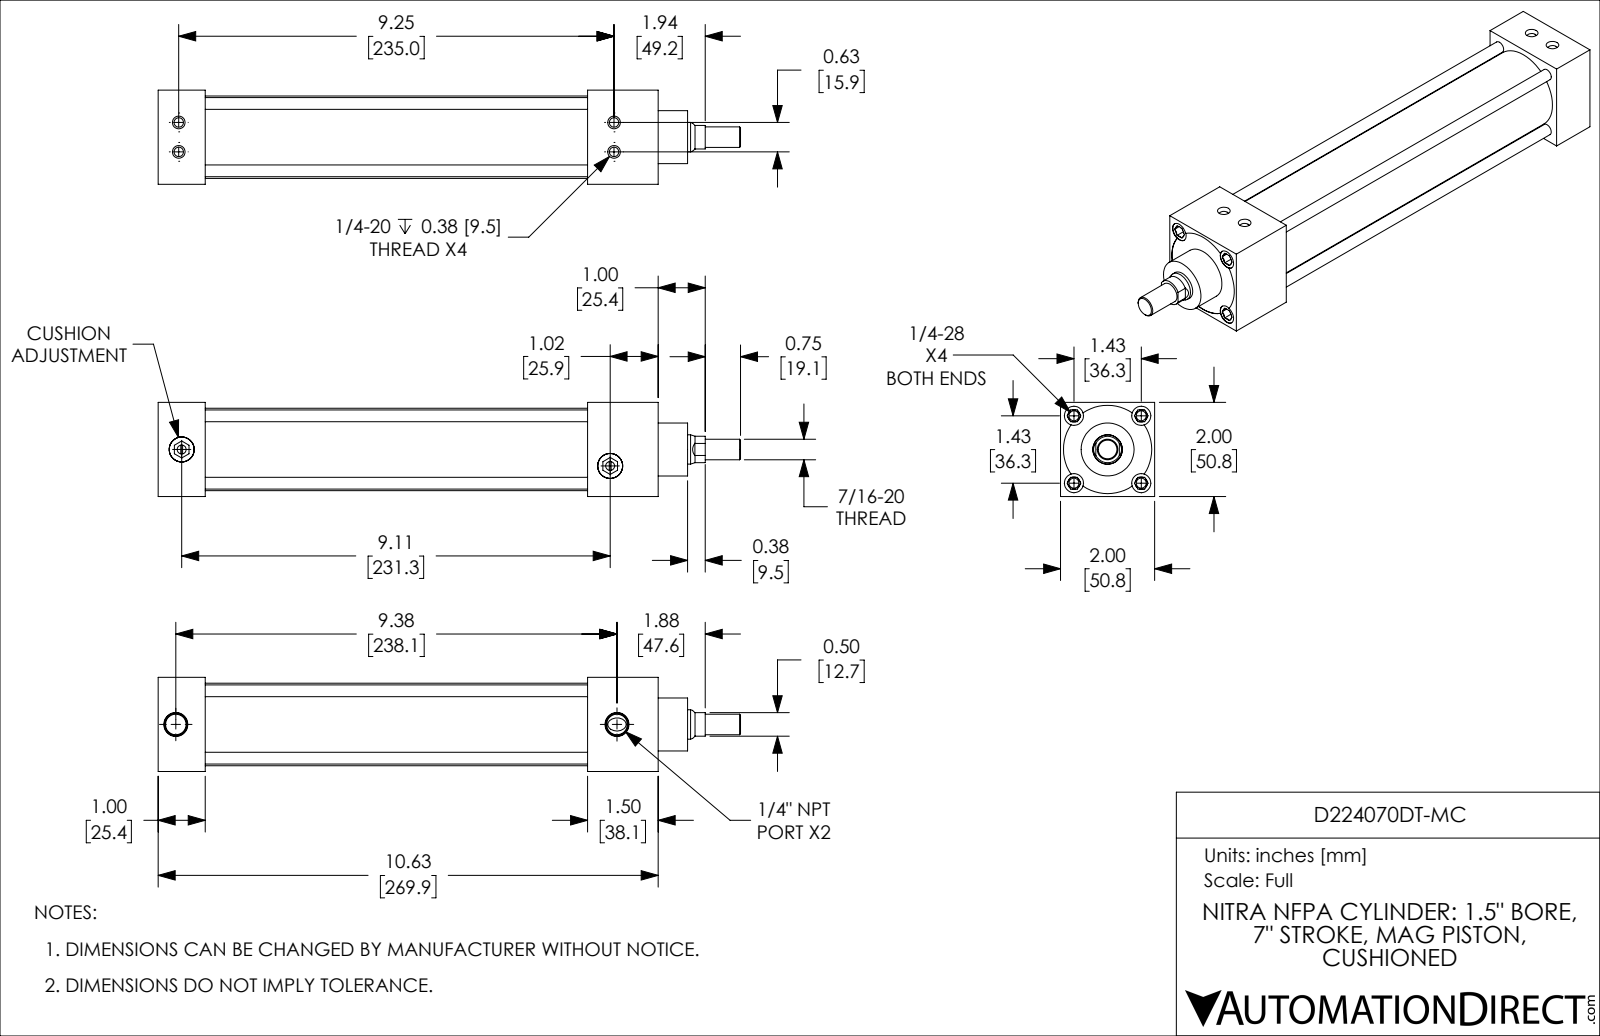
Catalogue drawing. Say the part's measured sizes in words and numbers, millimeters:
The part is named "D224070DT-MC_CUSHION; D224070DT-MC_BODY; D224070DT-MC; D224070DT-MC_PISTON_KK1". Its 3-D file was written by "SolidWorks 2019 (CONFIG_CONTROL_DESIGN)". It is 4 solids with 251 faces: 90 planar, 81 cylindrical and 80 other. Overall it measures 314.3 by 50.8 by 50.8 millimeters. Its volume is 346 800 cubic millimeters and its surface area 120 100 square millimeters. Round holes: 4 of diameter 5.1, 4 of diameter 5.4, 4 of diameter 10.3, 2 of diameter 4.8, 2 of diameter 11.1, 2 of diameter 13.5, 1 of diameter 15.9, 1 of diameter 38.1. Round bosses or shafts: 4 of diameter 6.4, 2 of diameter 13.5, 1 of diameter 44.5, 1 of diameter 38.1, 1 of diameter 28.6, 1 of diameter 15.8, 1 of diameter 11.1. Partial cylindrical surfaces (rounded edges, fillets, slot ends): 1 of radius 7.1, 1 of radius 23.8. The main face-to-face distances are 50.8, 25.4, 231.8, 206.4, 269.7, 244.3, 38, 28.6, 54, 177.8. The hole center spacings are 8.1, 25.7, 36.3, 15.9, 51.4, 235, 235.5, 236.7.
